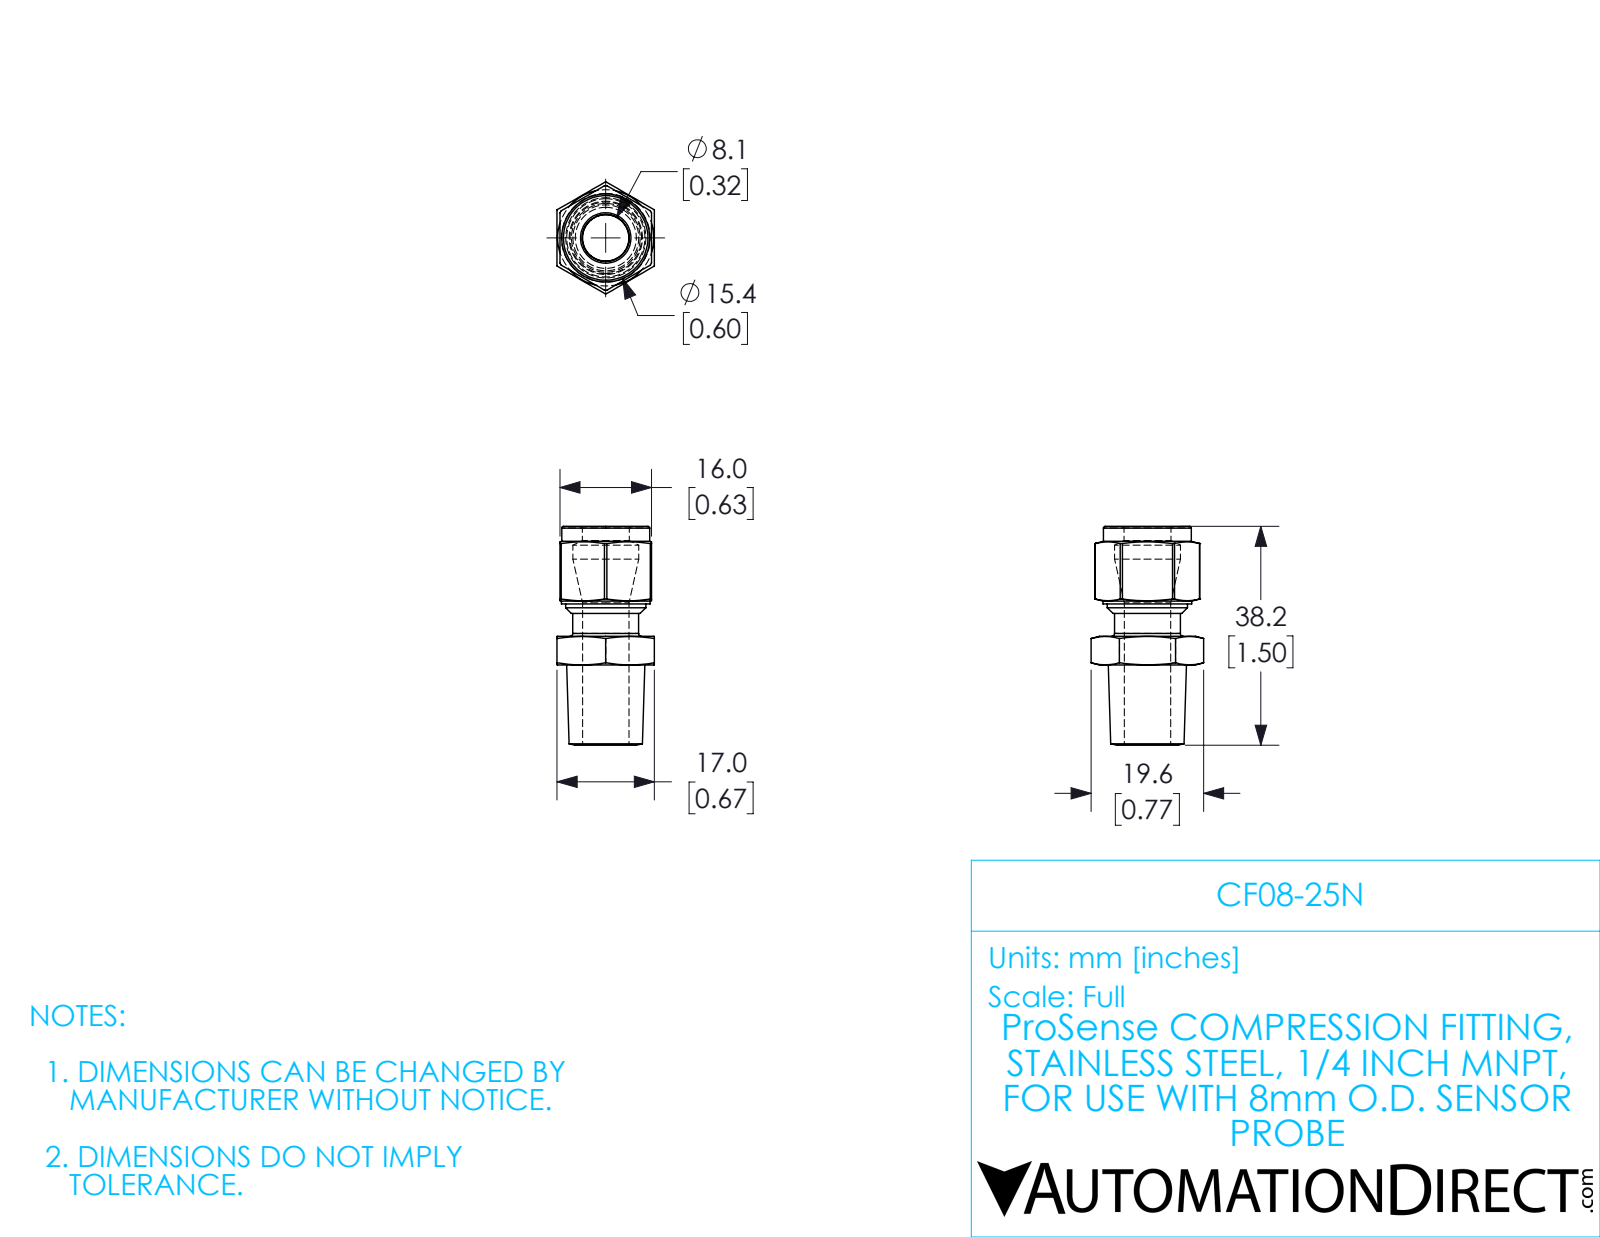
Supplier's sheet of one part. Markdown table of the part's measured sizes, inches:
| quantity | value |
| --- | --- |
| part name | CF08-25N |
| STEP written by | SolidWorks 2017 (AUTOMOTIVE_DESIGN) |
| units | inches |
| bodies | 1 solid, 63 faces (18 planar, 21 cylindrical, 24 other) |
| overall size | 1.504 × 0.773 × 0.669 |
| volume | 0.268 in³ |
| surface area | 5.31 in² |
| round holes (diameter × count) | 0.319 × 1, 0.323 × 1, 0.453 × 1 |
| round bosses / shafts (diameter × count) | 0.61 × 1, 0.605 × 1, 0.551 × 1 |
| partial cylindrical surfaces (radius × count) | 0.359 × 1 |
| main face-to-face distances | 0.02, 0.65, 0.63, 0.669, 0.756, 0.197, 0.953, 0.551, 0.748, 1.504 |
